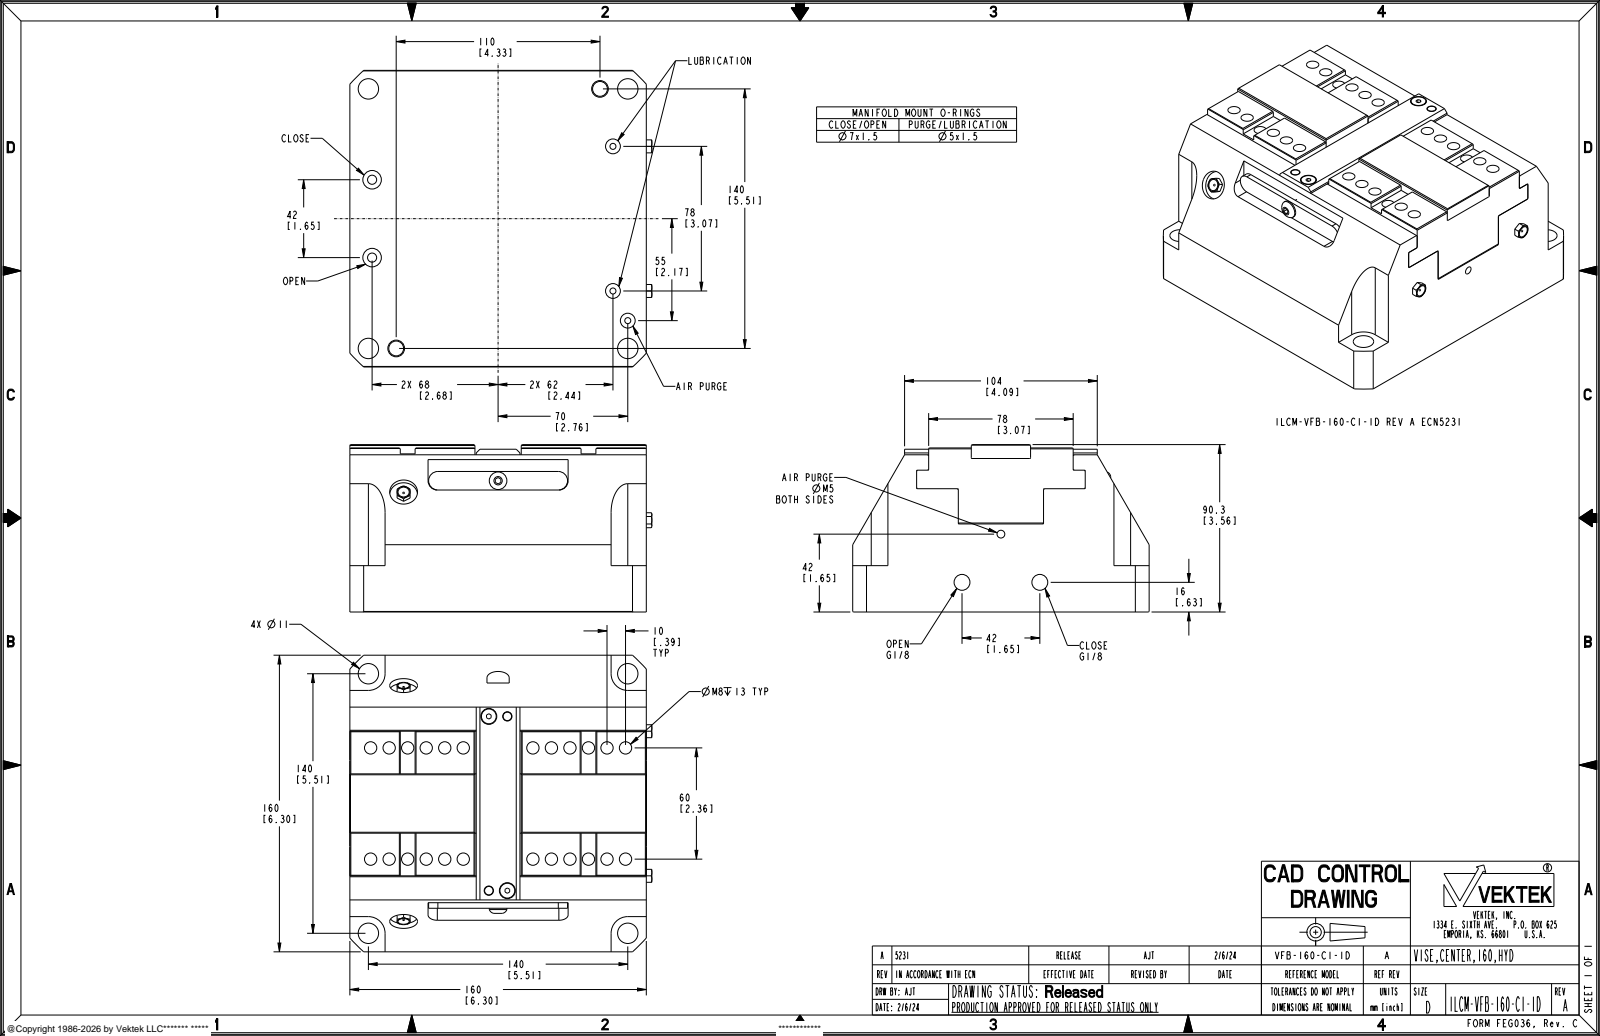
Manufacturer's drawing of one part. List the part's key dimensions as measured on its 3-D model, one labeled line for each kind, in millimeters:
Part name (STEP PRODUCT): CORPO; GRIFFA_C1; COPERCHIO; ISO_2338_-_5_H8_X_10_-_B_3 (+4 more)
STEP written by: CREO PARAMETRIC BY PTC INC, 2021164 (AUTOMOTIVE_DESIGN)
Units: millimetres
Bodies: 10 solids, 600 faces (275 planar, 171 cylindrical, 154 other)
Overall size (bounding box): 163 × 160 × 90.3
Volume: 1 895 000 mm³ · Surface area: 183 736 mm²
Round holes (diameter × count): ⌀6.65 ×24, ⌀3.3 ×5, ⌀8 ×5, ⌀11 ×4, ⌀3.24 ×3, ⌀4 ×2, ⌀4.2 ×2, ⌀4.92 ×2, ⌀5 ×2, ⌀8.57 ×2, ⌀10 ×2, ⌀15 ×2
Round bosses / shafts (diameter × count): ⌀8 ×2, ⌀9.5 ×1, ⌀5 ×1
Partial cylindrical surfaces — rounded edges, fillets, slot ends (radius × count): R0.4 ×10, R2.6 ×4, R3.6 ×4, R5 ×4, R9 ×4, R6 ×1, R108 ×1
Main face-to-face distances: 19, 66.5, 160, 47.5, 41, 57, 103, 18.3, 84.8, 37.3
Hole centre spacings: 10, 60.83, 20, 63.25, 30, 29.24, 60, 67.08
